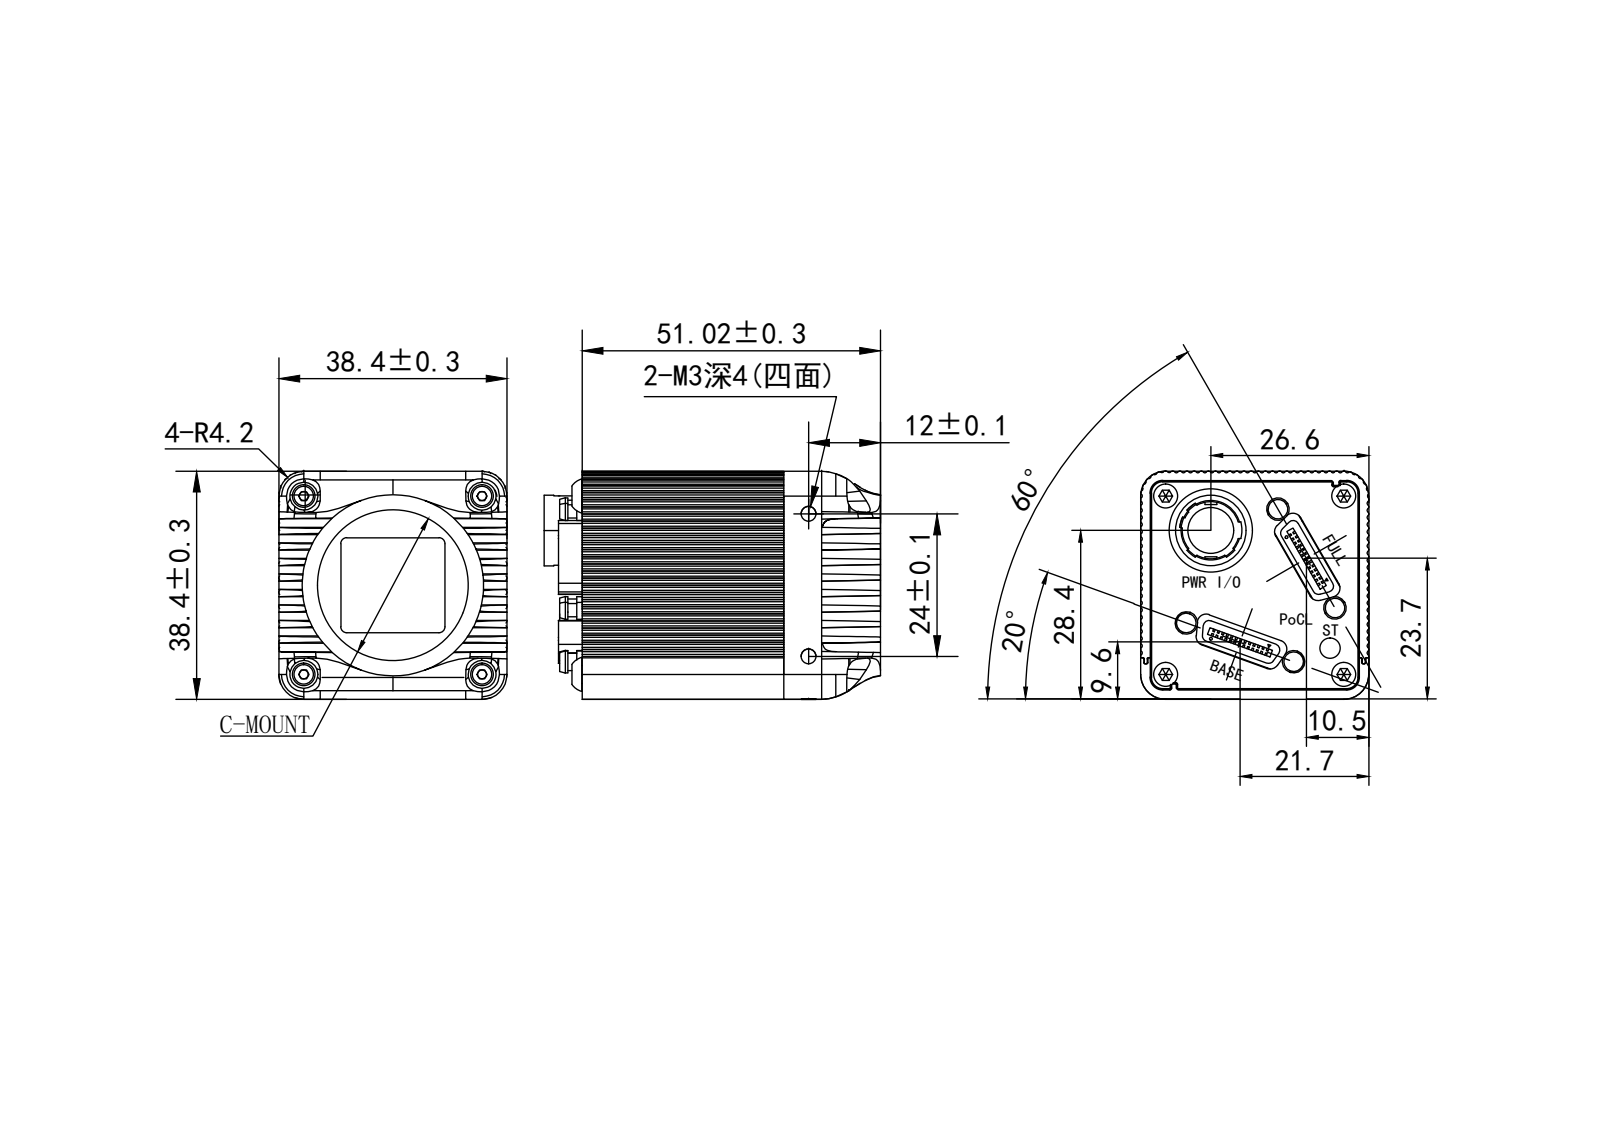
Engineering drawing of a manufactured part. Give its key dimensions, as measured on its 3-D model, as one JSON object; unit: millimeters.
{"step_written_by": "SolidWorks 2019 (AUTOMOTIVE_DESIGN)", "units": "millimeters", "bodies": {"solids": 17, "faces": 2270, "planar": 1303, "cylindrical": 751, "other": 216}, "overall_size": [57.38, 38.41, 38.4], "volume_mm3": 66549, "surface_area_mm2": 29096, "round_holes": [[0.8, 12], [2.2, 8], [1.6, 4], [2.5, 4], [4.7, 4], [0.5, 2], [3.2, 1], [7.7, 1], [8.6, 1], [10, 1], [11.1, 1], [12.4, 1]], "round_bosses_or_shafts": [[1.1, 12], [3.8, 8], [3, 5], [2, 4], [14, 1], [11.9, 1], [11, 1], [10.5, 1]], "partial_cylinders_radius": [[0.4, 162], [0.3, 89], [0.2, 32], [0.5, 28], [0.18, 24], [1.5, 20], [1, 12], [5.6, 12]], "face_to_face_distances": [2, 31.92, 7, 31.74, 31.84, 1.82, 33.74, 1.9, 1.7, 30.02], "hole_center_spacings": [2.75, 1.88, 4.76, 5.42, 3.54, 1.1, 1.76, 2.4]}
